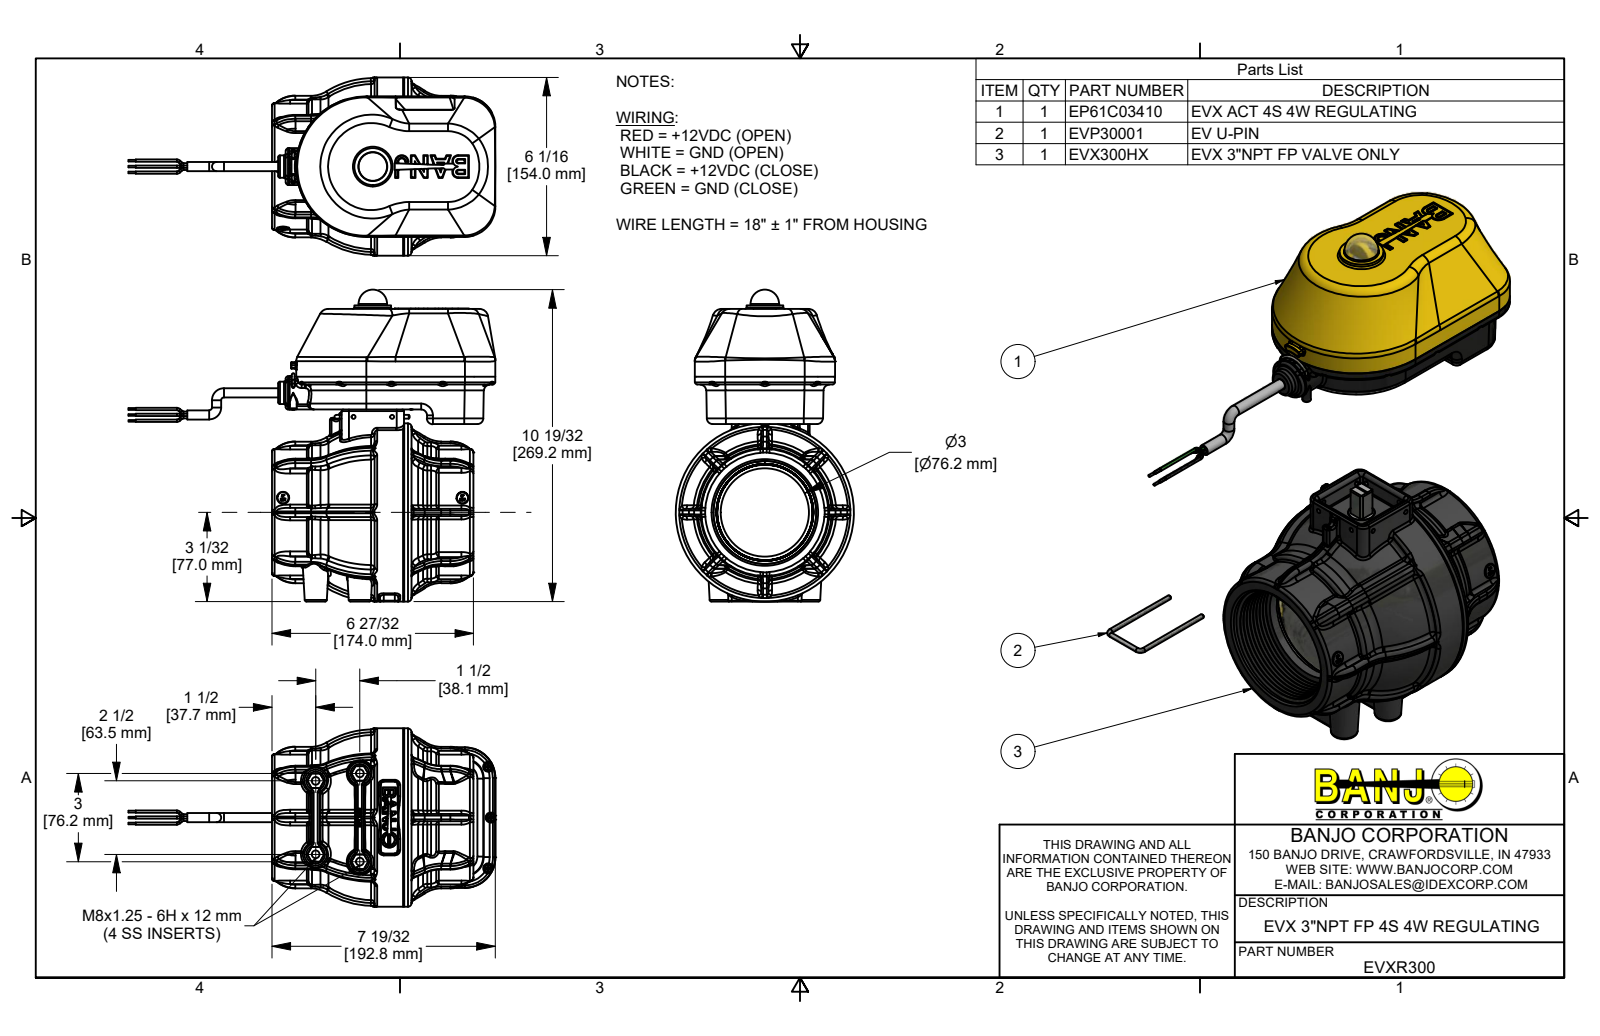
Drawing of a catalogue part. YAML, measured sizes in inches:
part_name: "EVXR300; EP61C03410; 91400A119; 91841A005 (+8 more)"
step_written_by: "Autodesk Inventor 2019 (AUTOMOTIVE_DESIGN)"
units: inches
bodies: {solids: 78, faces: 10226, planar: 3741, cylindrical: 3183, other: 3302}
overall_size: [61.255, 10.6, 6.063]
volume: 96.29
surface_area: 2741
round_holes:
  - {diameter: 0.095, count: 11}
  - {diameter: 0.15, count: 11}
  - {diameter: 0.34, count: 11}
  - {diameter: 0.135, count: 6}
  - {diameter: 0.104, count: 4}
  - {diameter: 0.136, count: 4}
  - {diameter: 0.176, count: 4}
  - {diameter: 0.262, count: 4}
  - {diameter: 0.266, count: 4}
  - {diameter: 0.433, count: 4}
  - {diameter: 0.089, count: 2}
  - {diameter: 0.105, count: 2}
round_bosses_or_shafts:
  - {diameter: 0.08, count: 20}
  - {diameter: 0.25, count: 19}
  - {diameter: 0.14, count: 11}
  - {diameter: 0.108, count: 11}
  - {diameter: 0.085, count: 11}
  - {diameter: 0.058, count: 8}
  - {diameter: 0.437, count: 4}
  - {diameter: 0.375, count: 4}
partial_cylinders:
  - {radius: 0.405, count: 138}
  - {radius: 0.387, count: 114}
  - {radius: 0.309, count: 112}
  - {radius: 0.253, count: 108}
  - {radius: 0.609, count: 106}
  - {radius: 0.125, count: 74}
  - {radius: 0.01, count: 68}
  - {radius: 0.06, count: 49}
face_to_face_distances: [0.083, 0.5, 0.085, 0.181, 0.096, 2.175, 2.356, 2.271, 0.125, 2.481]
hole_center_spacings: [3.316, 1.115, 1.313, 2.259, 0.55, 0.611, 0.646, 0.663]
